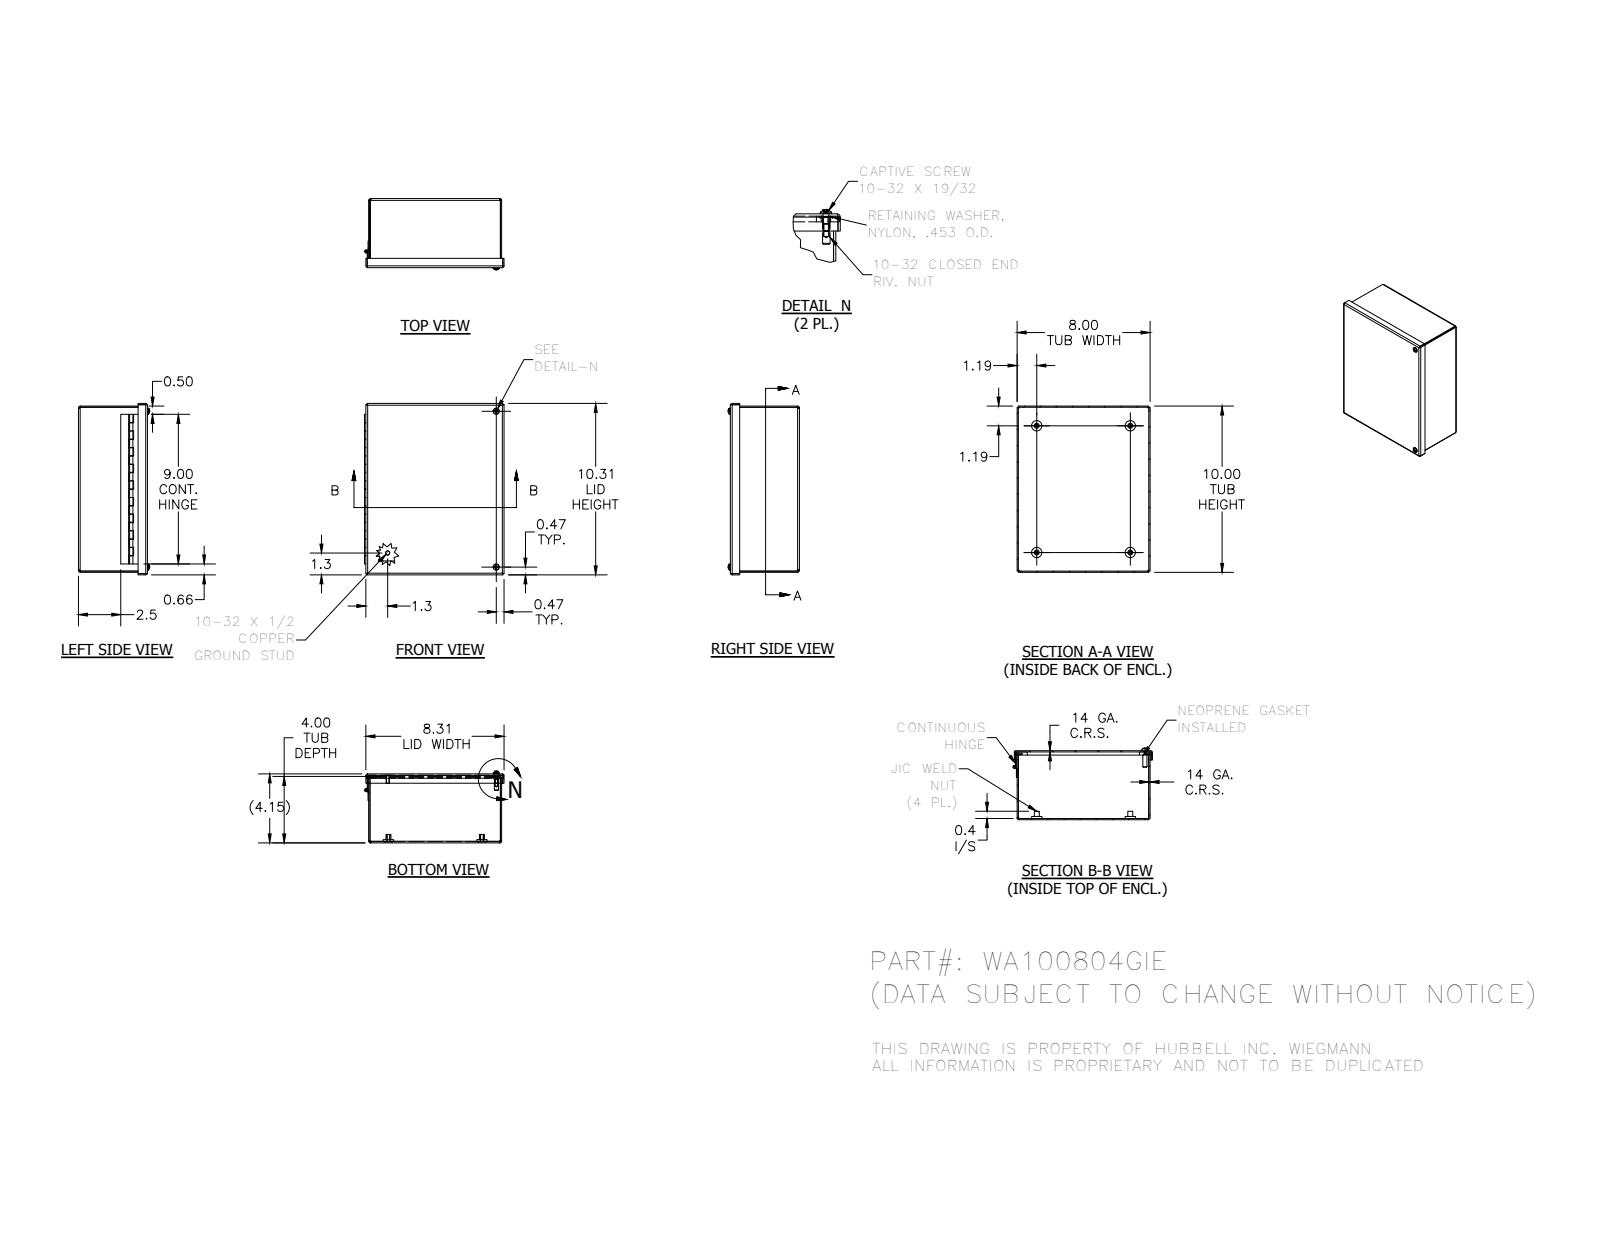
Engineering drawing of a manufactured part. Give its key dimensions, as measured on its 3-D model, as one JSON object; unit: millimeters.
{"part_name": "WA100804GIEBKP; 3499; 328122LH; 328122P (+8 more)", "step_written_by": "Autodesk Inventor 2014 (AUTOMOTIVE_DESIGN)", "units": "millimeters", "bodies": {"solids": 18, "faces": 465, "planar": 269, "cylindrical": 121, "other": 75}, "overall_size": [261.94, 213.28, 108.77], "volume_mm3": 492312, "surface_area_mm2": 500241, "round_holes": [[3.96, 6], [6.53, 4], [7.94, 4], [4.98, 2], [7.06, 2], [7.14, 2], [2.96, 1]], "round_bosses_or_shafts": [[15.88, 4], [7.62, 4], [4.83, 3], [11.51, 2], [10.31, 2], [9.47, 2], [6.3, 2], [6.35, 1]], "partial_cylinders_radius": [[0.79, 12], [2.67, 12], [1.78, 8], [2.27, 2]], "face_to_face_distances": [1.88, 103.58, 101.7, 105.46, 201.32, 252.12, 203.2, 199.44, 254, 250.24], "hole_center_spacings": [238.12, 31.42, 166.59, 187.32, 238.11, 187.61, 217.04, 271.79]}
